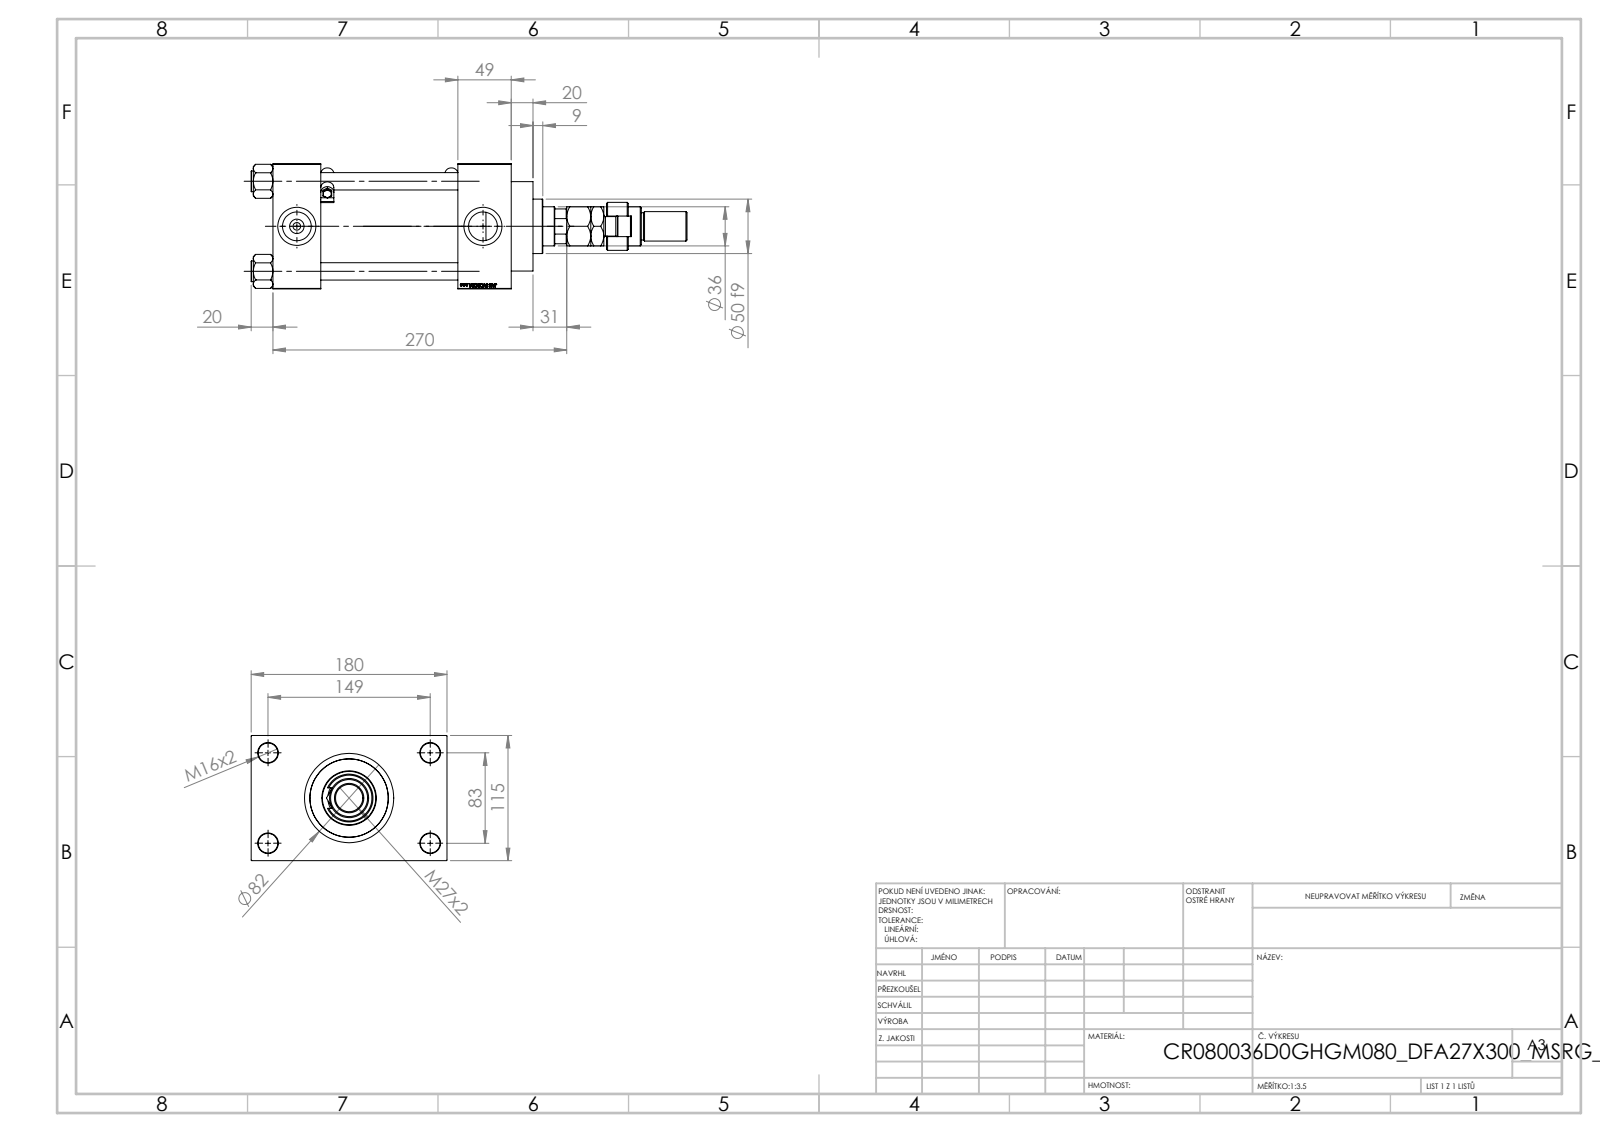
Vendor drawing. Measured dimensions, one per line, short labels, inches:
name: NUT_M5_D; MSRF_MSRG1; MFA; FEMALE_PART_FOR_DFA (+4 more)
written by: SolidWorks 2019 (CONFIG_CONTROL_DESIGN)
unit: in
bodies: 15 solids, 1300 faces (609 planar, 129 cylindrical, 562 other)
size: 15.768 × 7.087 × 4.528
volume: 136.8 in³; area: 577.5 in²
holes: 4× ⌀0.63, 4× ⌀0.709, 2× ⌀0.276, 2× ⌀1.041, 2× ⌀1.378, 1× ⌀1.004, 1× ⌀1.535, 1× ⌀2.402, 1× ⌀2.835, 1× ⌀3.15
bosses: 4× ⌀0.748, 2× ⌀0.197, 2× ⌀0.098, 1× ⌀3.386, 1× ⌀3.228, 1× ⌀1.969, 1× ⌀1.732, 1× ⌀1.417
rounds: 12× R0.02, 4× R0.236, 1× R0.374, 1× R0.591, 1× R0.689
face distances: 4.528, 4.961, 6.89, 1.929, 6.693, 1.732, 8.622, 1.28, 5.807, 7.087
hole spacings: 1.305, 2.302, 3.256, 3.357, 3.513, 4.561, 5.607, 3.268
